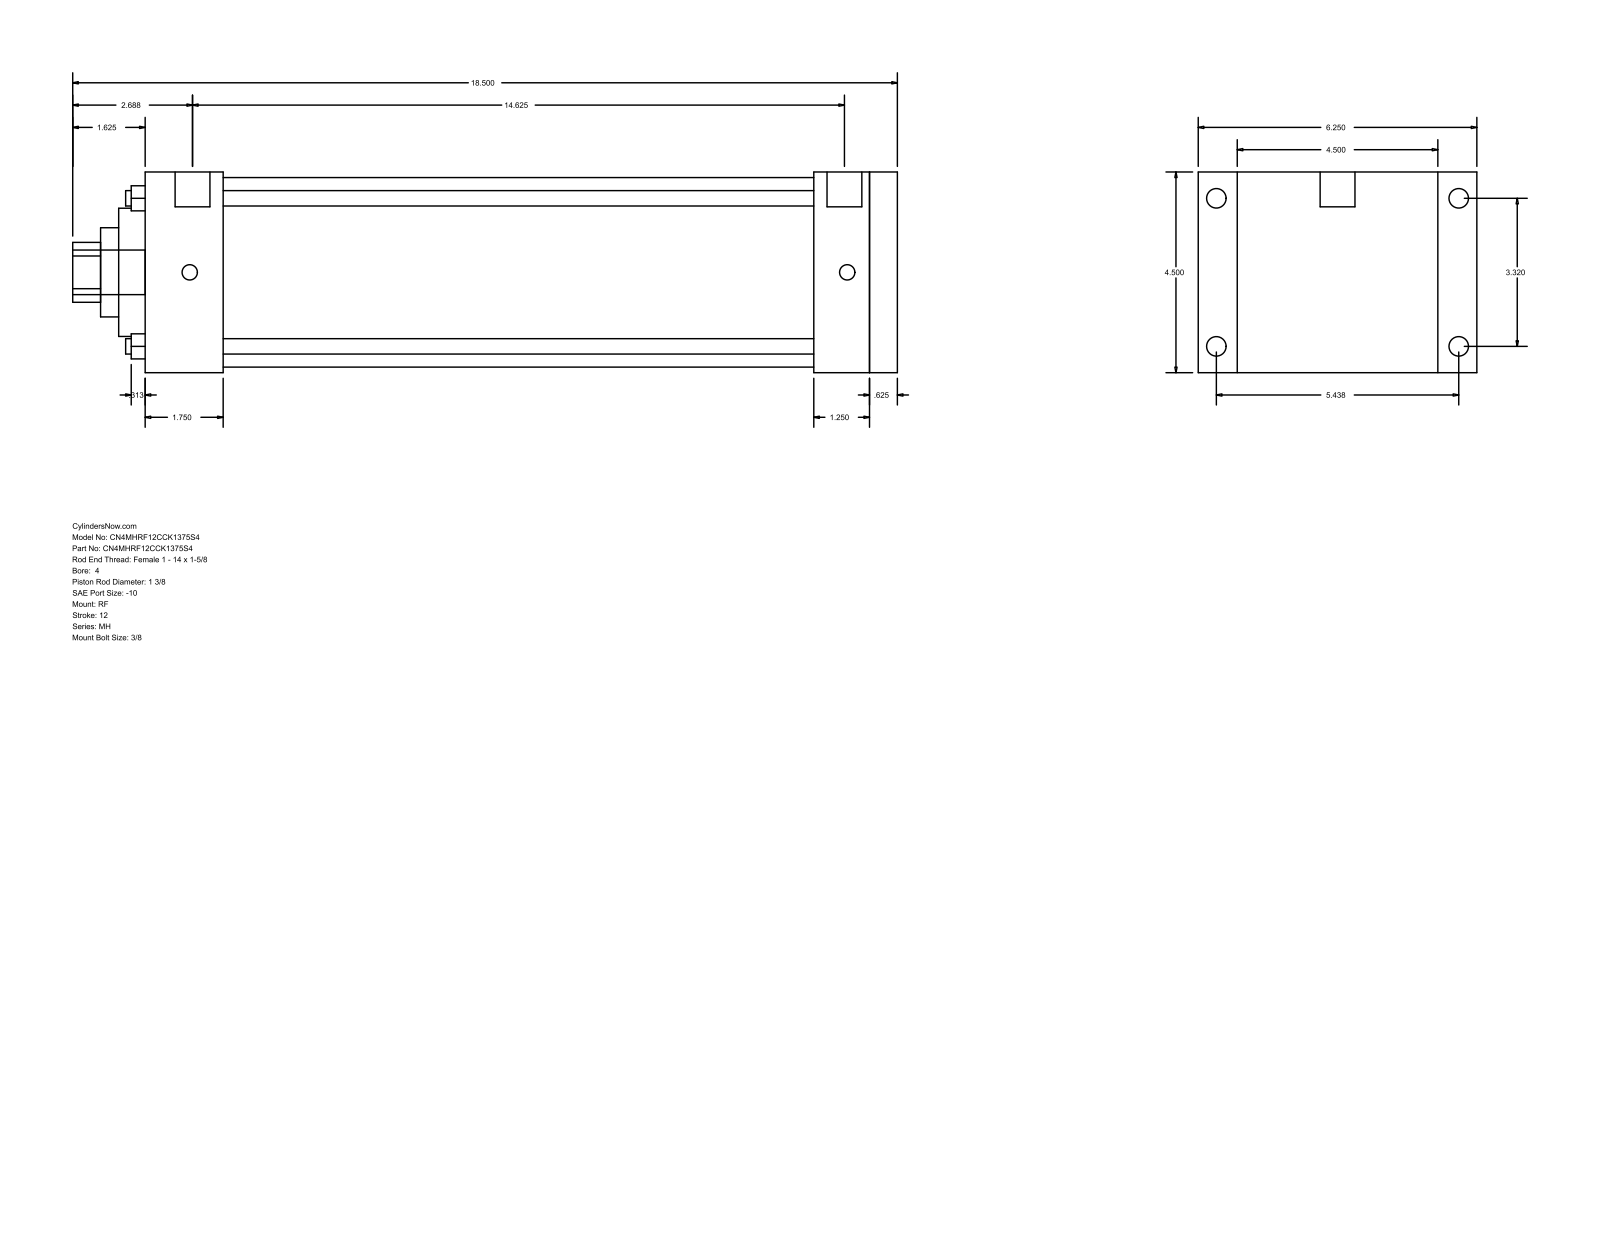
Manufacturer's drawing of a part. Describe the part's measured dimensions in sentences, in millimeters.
The part is named "MH_RF__0400_1.375". Its 3-D file was written by "GSSL Pune (CONFIG_CONTROL_DESIGN)". It is 0 solids with 94 faces: 65 planar, 29 cylindrical and 0 other. Overall it measures 469.9 by 158.75 by 114.3 millimeters. Round holes: 4 of diameter 8.76, 1 of diameter 34.92, 1 of diameter 50.8, 1 of diameter 73.03, 1 of diameter 107.95. Round bosses or shafts: 4 of diameter 11.13, 4 of diameter 8.73, 2 of diameter 19.84, 1 of diameter 25.4. Partial cylindrical surfaces (rounded edges, fillets, slot ends): 1 of radius 17.06. The main face-to-face distances are 114.3, 428.63, 15.88, 412.75, 44.45, 368.3, 384.18, 381, 336.55, 31.75. The hole center spacings are 59.62, 84.32, 119.25.
